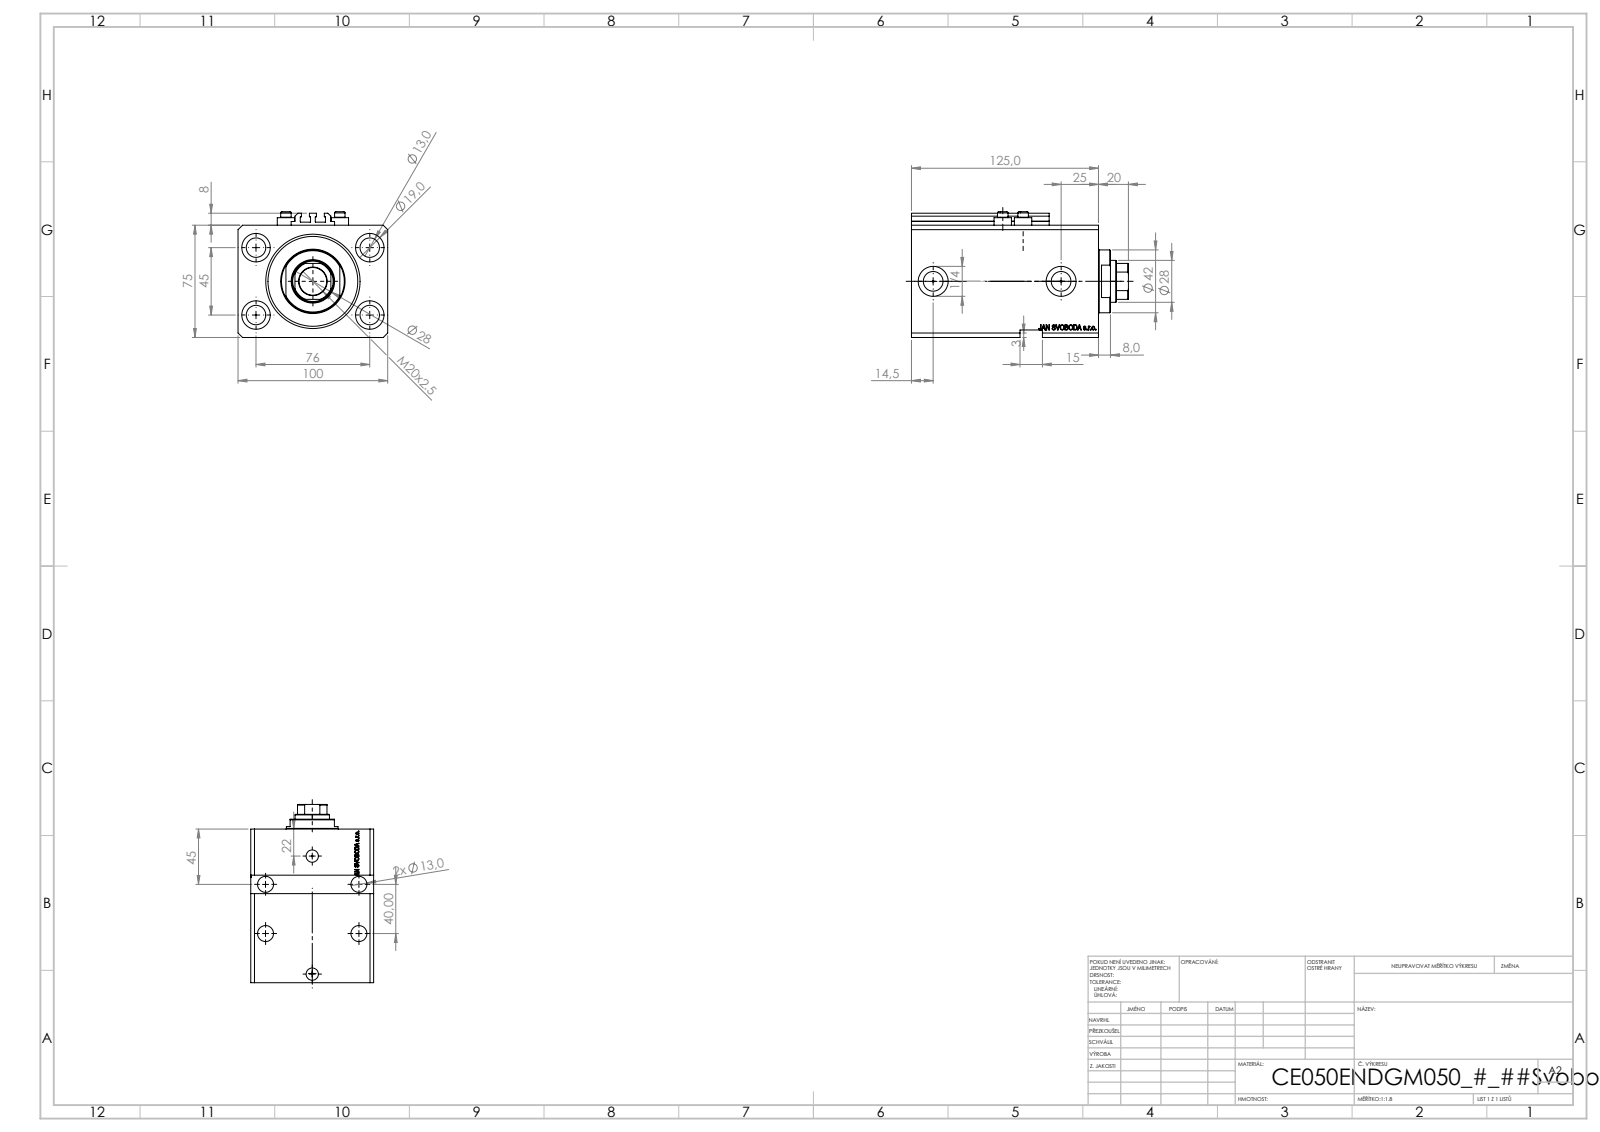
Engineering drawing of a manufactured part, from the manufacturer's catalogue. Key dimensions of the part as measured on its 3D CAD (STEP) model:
Part name (STEP PRODUCT): V250CE_C_VCP; V250CE_E_Body; ALLEN BOLT V250CE; V250CE_VC_E
STEP written by: SolidWorks 2019 (CONFIG_CONTROL_DESIGN)
Units: millimetres
Bodies: 8 solids, 1124 faces (539 planar, 158 cylindrical, 427 other)
Overall size (bounding box): 145 × 100 × 84
Volume: 765 184 mm³ · Surface area: 151 526 mm²
Round holes (diameter × count): ⌀13 ×8, ⌀1.25 ×4, ⌀4 ×4, ⌀19 ×4, ⌀10 ×2, ⌀13.16 ×2, ⌀20 ×2, ⌀18.5 ×1, ⌀28 ×1, ⌀50 ×1, ⌀63 ×1
Round bosses / shafts (diameter × count): ⌀11.6 ×4, ⌀7 ×4, ⌀42 ×1
Partial cylindrical surfaces — rounded edges, fillets, slot ends (radius × count): R0.2 ×10, R13.5 ×1
Main face-to-face distances: 75, 100, 125, 20, 11.9, 113.1, 105, 93.1, 70, 13
Hole centre spacings: 44.16, 76, 13.6, 20.72, 27.59, 29, 33.62, 36
